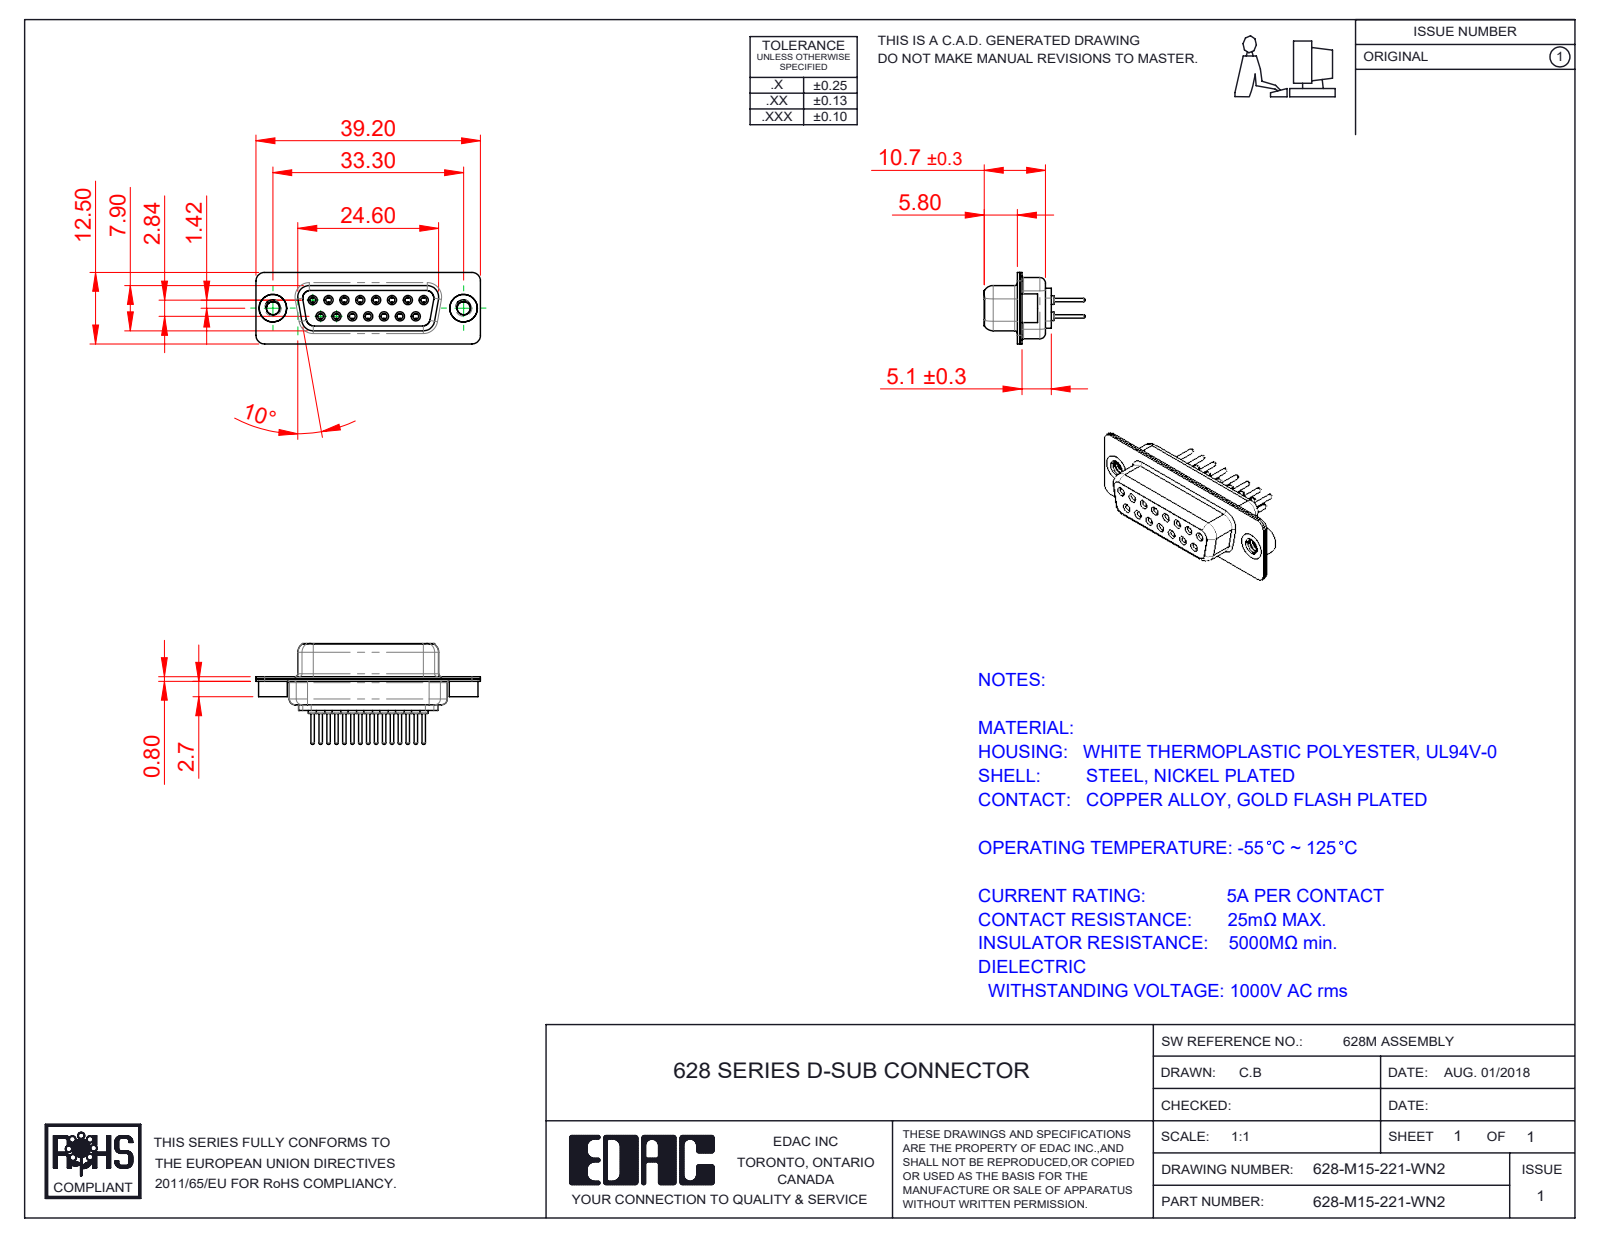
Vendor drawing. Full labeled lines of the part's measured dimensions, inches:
Part name (STEP PRODUCT): 628-M15-221-WN2; 628M Contact Row 2_21; 628M Shell Rear_15 Contacts; 628M Contact Row 1_21 (+3 more)
STEP written by: SolidWorks 2020 (CONFIG_CONTROL_DESIGN)
Units: inches
Bodies: 20 solids, 1104 faces (292 planar, 422 cylindrical, 390 other)
Overall size (bounding box): 1.543 × 0.693 × 0.492
Volume: 0.151 in³ · Surface area: 9.616 in²
Round holes (diameter × count): ⌀0.039 ×15, ⌀0.043 ×15, ⌀0.067 ×15, ⌀0.071 ×15, ⌀0.079 ×15, ⌀0.089 ×2, ⌀0.157 ×2, ⌀0.189 ×2
Round bosses / shafts (diameter × count): ⌀0.087 ×15, ⌀0.063 ×15, ⌀0.059 ×15, ⌀0.024 ×15, ⌀0.197 ×2, ⌀0.193 ×2
Partial cylindrical surfaces — rounded edges, fillets, slot ends (radius × count): R0.059 ×16, R0.079 ×12, R0.053 ×8, R0.063 ×8, R0.01 ×4, R0.02 ×4, R0.024 ×4, R0.026 ×4
Main face-to-face distances: 0.016, 0.055, 0.018, 0.333, 0.35, 0.071, 0.244, 0.039, 0.278, 0.073
Hole centre spacings: 0.124, 0.109, 0.218, 0.327, 0.436, 0.198, 0.198, 0.294
